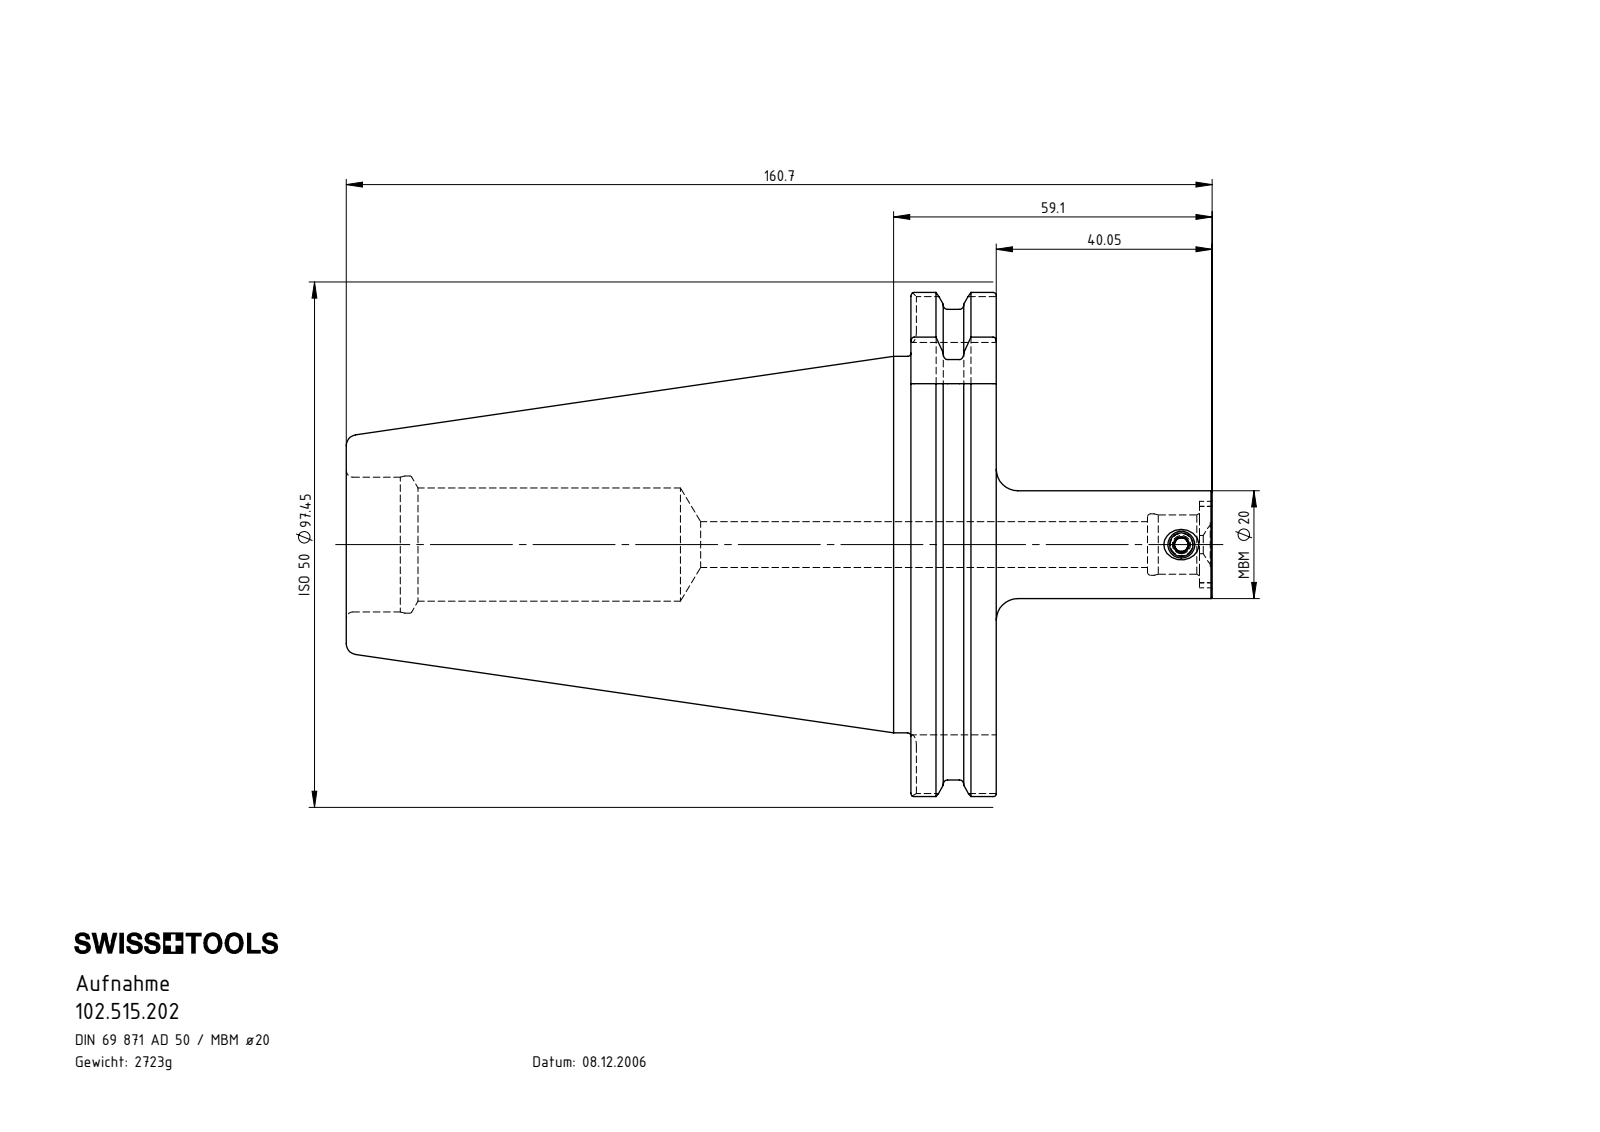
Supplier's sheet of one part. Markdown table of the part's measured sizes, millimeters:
| quantity | value |
| --- | --- |
| part name | SK5-MB1.K01.059_B; MB1-ER1.001.006_A; 102.515.202 |
| STEP written by | SolidWorks 2017 (CONFIG_CONTROL_DESIGN) |
| units | millimeters |
| bodies | 2 solids, 172 faces (53 planar, 50 cylindrical, 69 other) |
| overall size | 160.7 × 97.45 × 93.51 |
| volume | 346 851 mm³ |
| surface area | 44 802 mm² |
| round holes (diameter × count) | 2.5 × 1, 4.2 × 1, 8.5 × 1, 11 × 1, 11.4 × 1, 21 × 1, 25 × 1, 25.45 × 1 |
| round bosses / shafts (diameter × count) | 91 × 1, 69.85 × 1, 20 × 1, 5 × 1 |
| partial cylindrical surfaces (radius × count) | 2 × 8, 2.2 × 4, 6.5 × 1, 8.03 × 1, 48.73 × 1 |
| main face-to-face distances | 15.85, 104.8, 120.65, 72.8, 25.7, 42.7, 17, 7.65, 65.15, 160.7 |
